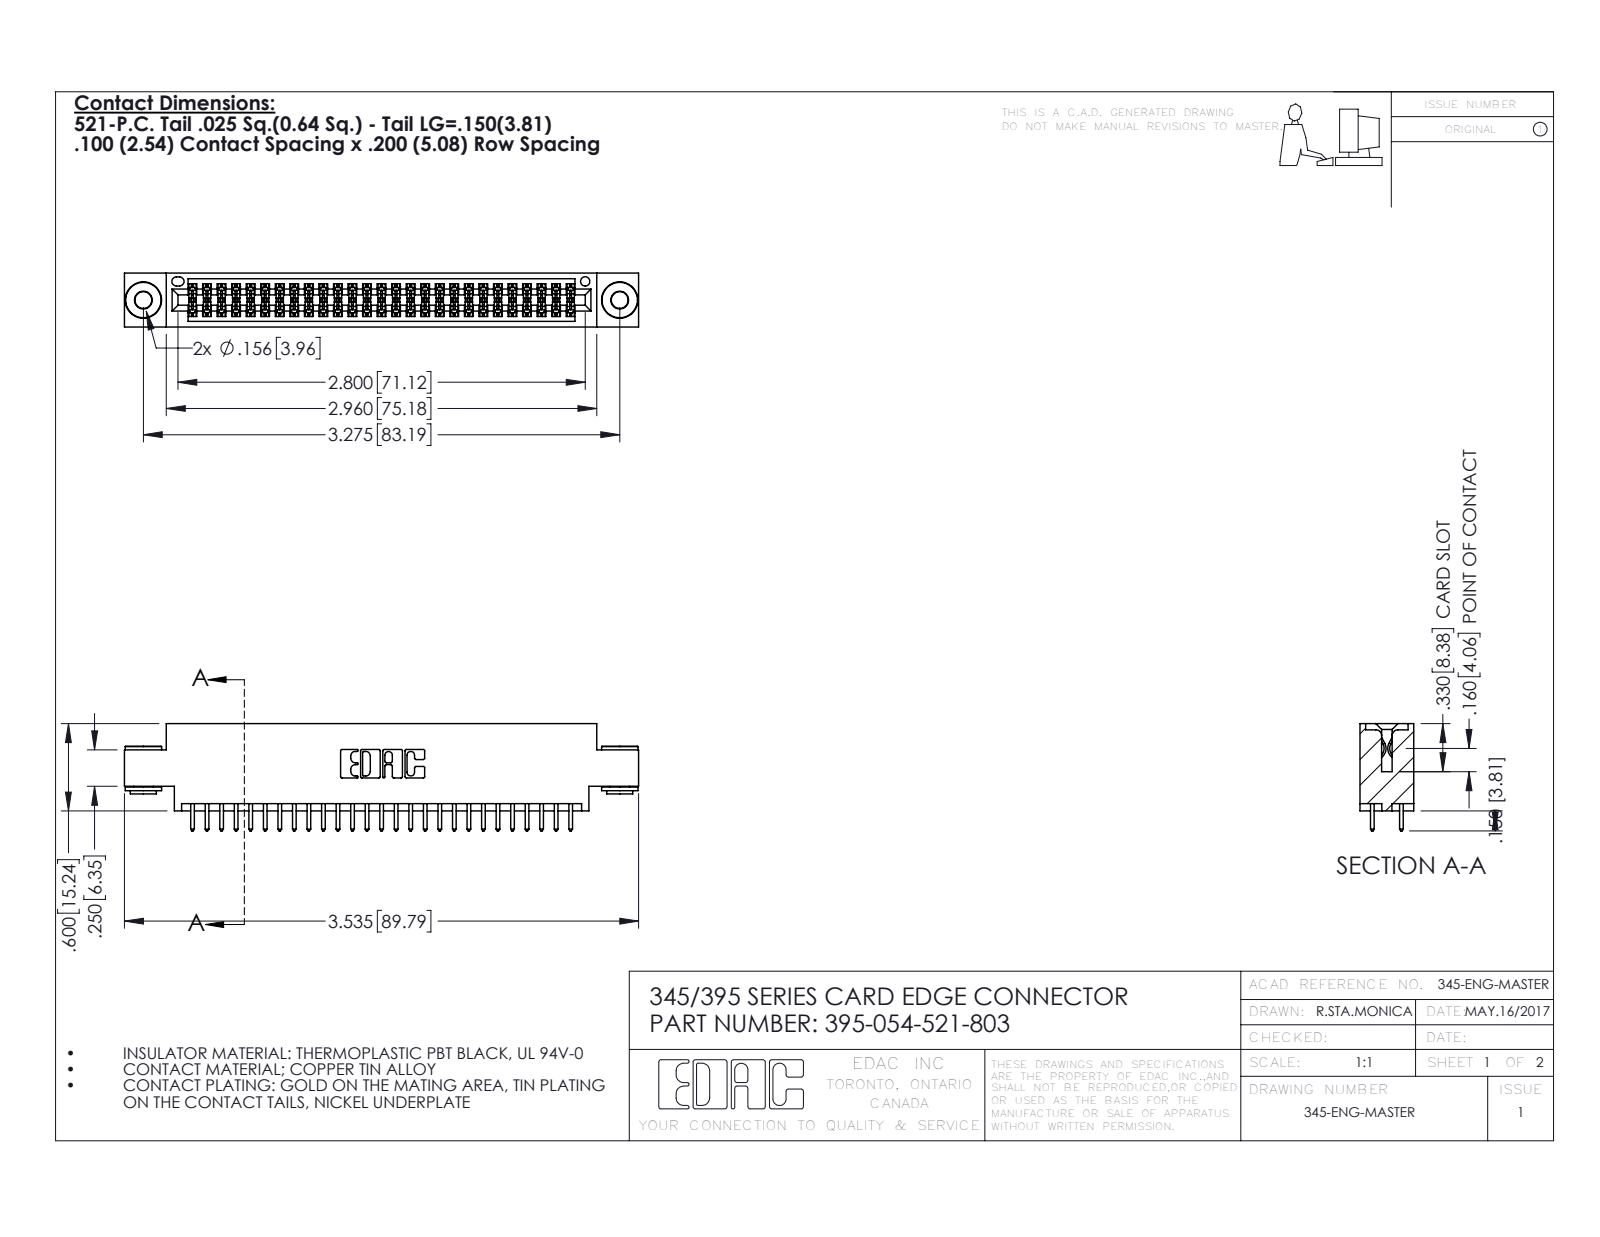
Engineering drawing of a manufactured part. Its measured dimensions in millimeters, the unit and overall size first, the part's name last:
Units: millimetres
Overall size (bounding box): 89.8 × 18.7 × 9.4
Round holes (diameter × count): ⌀2.9 ×2, ⌀4 ×2, ⌀1.6 ×1
Round bosses / shafts (diameter × count): ⌀6.4 ×2, ⌀4.6 ×2, ⌀3.5 ×2
Partial cylindrical surfaces — rounded edges, fillets, slot ends (radius × count): R0.2 ×81, R0.3 ×54, R0.3 ×22, R0.2 ×6, R0.8 ×6, R0.7 ×3, R0.4 ×2, R0.5 ×2
Main face-to-face distances: 1.8, 7.6, 9.4, 5.1, 2.5, 6.9, 0.6, 5.7, 4.4, 2.5
Hole centre spacings: 6.9, 77.2, 83.2
Volume: 8 470 mm³ · Surface area: 12 430 mm²
Bodies: 57 solids, 2868 faces (1876 planar, 984 cylindrical, 8 other)
Part name (STEP PRODUCT): 345 Part_0.170 Offset - 0.156 Dia-TH; 395-054-521-803; 345-292-001_345-293-121; 345-250-002_345-250-002-102
STEP written by: SolidWorks 2016 (CONFIG_CONTROL_DESIGN)
